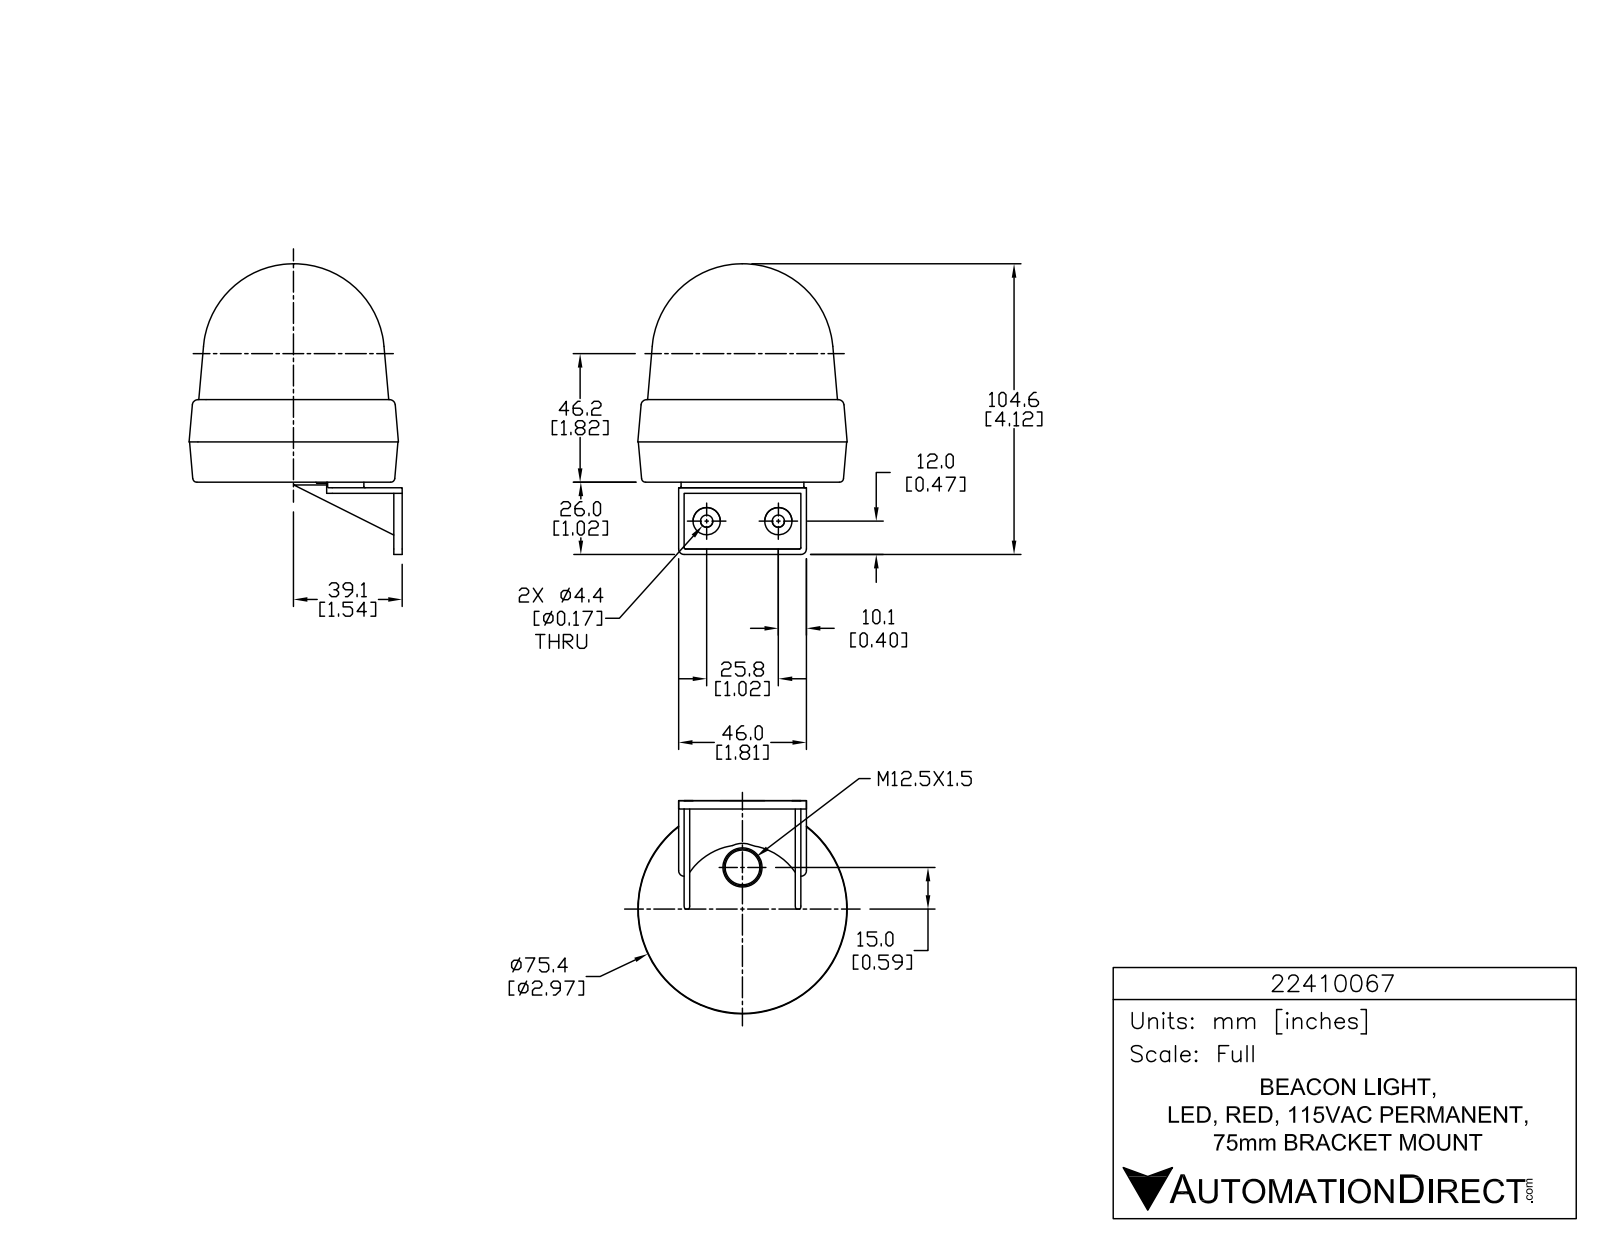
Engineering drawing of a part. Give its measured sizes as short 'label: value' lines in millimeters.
name: 22410067
written by: SolidWorks 2015 (AUTOMOTIVE_DESIGN)
unit: mm
bodies: 1 solid, 819 faces (549 planar, 180 cylindrical, 90 other)
size: 104.6 × 82.6 × 75.4
volume: 262 500 mm³; area: 27 080 mm²
holes: 3× ⌀1.5, 2× ⌀4.4
bosses: 3× ⌀8.6, 3× ⌀2.1, 2× ⌀9.8
rounds: 9× R0.1, 6× R0.1, 6× R0.3, 6× R0.3, 6× R0.3, 6× R0.5, 6× R5, 4× R2
face distances: 2, 4, 40, 1, 3, 42, 38, 2, 42, 44
hole spacings: 25.8
